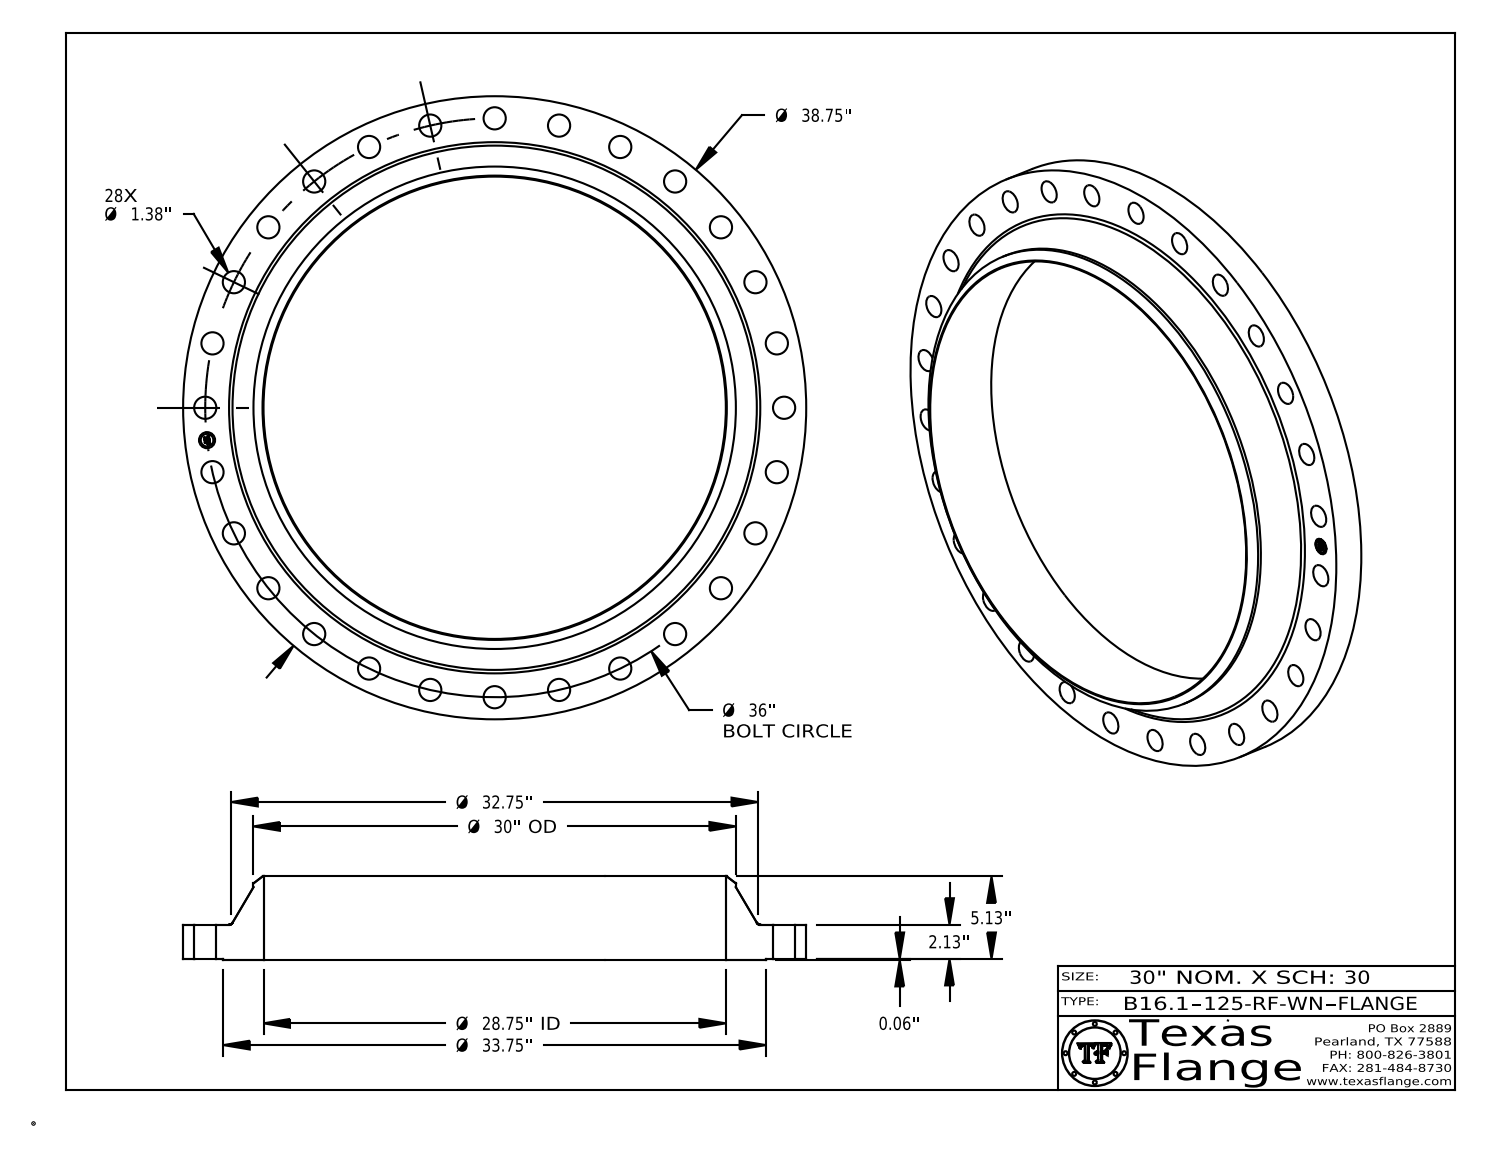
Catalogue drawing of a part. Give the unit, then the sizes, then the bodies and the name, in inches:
Units: inches
Overall size (bounding box): 38.75 × 38.75 × 5.193
Round holes (diameter × count): ⌀1.38 ×28, ⌀1 ×1, ⌀28.75 ×1
Round bosses / shafts (diameter × count): ⌀0.061 ×8, ⌀38.75 ×1, ⌀33.75 ×1, ⌀30 ×1, ⌀0.788 ×1
Main face-to-face distances: 2.193, 0.063, 2.13, 5.193, 5.13, 3, 0.015, 2.178, 2.115, 3.015
Hole centre spacings: 18, 19.153, 4.031, 8.011, 11.89, 15.62, 22.446, 25.456
Volume: 1 373 in³ · Surface area: 2 135 in²
Bodies: 1 solid, 459 faces (369 planar, 84 cylindrical, 6 other)
Part name (STEP PRODUCT): B16.1, Class 125-RF-WN
STEP written by: CATIA V5 STEP AP214 (AUTOMOTIVE_DESIGN)
